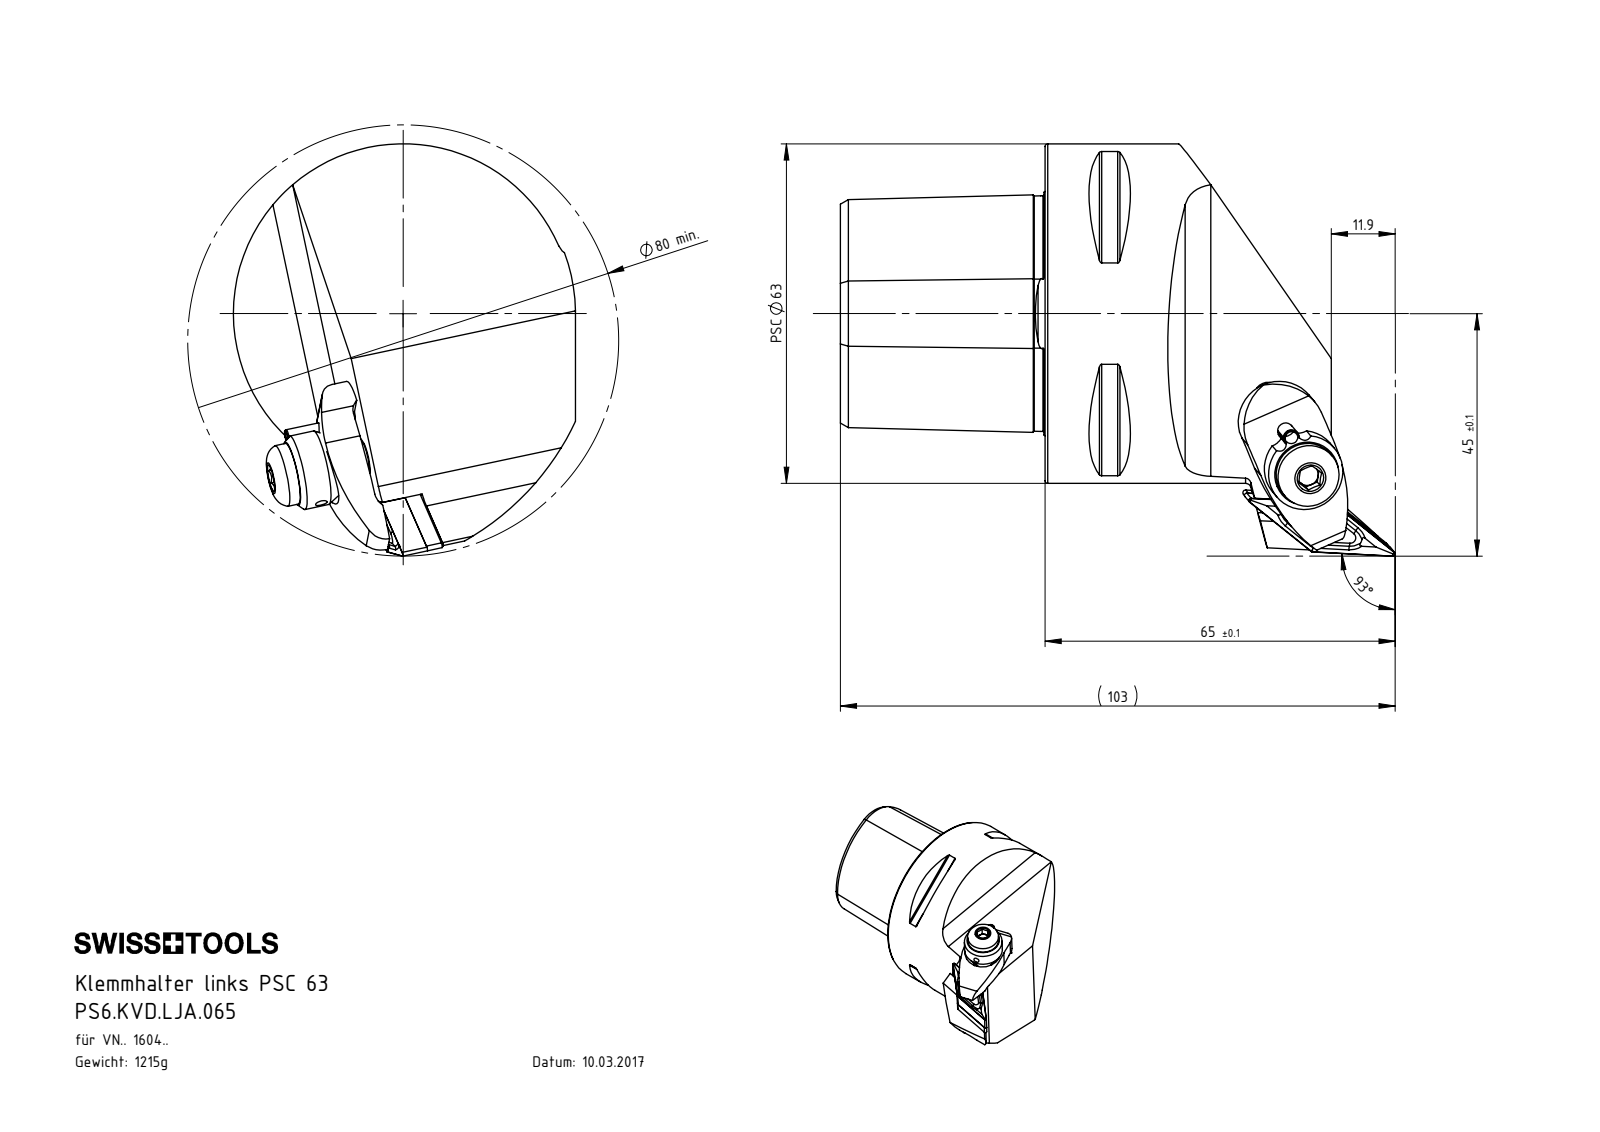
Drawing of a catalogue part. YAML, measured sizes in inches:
part_name: "KVT_MB_600_060; PS6.KVD.LJA.065; PS6-KVD.LJA.065_A; WCC-ER3.102.024_C (+7 more)"
step_written_by: "SolidWorks 2017 (AUTOMOTIVE_DESIGN)"
units: inches
bodies: {solids: 13, faces: 319, planar: 106, cylindrical: 89, other: 124}
overall_size: [4.055, 3.012, 2.5]
volume: 9.409
surface_area: 49.88
round_holes:
  - {diameter: 0.079, count: 3}
  - {diameter: 0.197, count: 3}
  - {diameter: 0.276, count: 2}
  - {diameter: 0.094, count: 1}
  - {diameter: 0.118, count: 1}
  - {diameter: 0.13, count: 1}
  - {diameter: 0.15, count: 1}
  - {diameter: 0.157, count: 1}
  - {diameter: 0.195, count: 1}
  - {diameter: 0.236, count: 1}
  - {diameter: 0.244, count: 1}
  - {diameter: 0.272, count: 1}
round_bosses_or_shafts:
  - {diameter: 0.236, count: 2}
  - {diameter: 0.157, count: 2}
  - {diameter: 0.118, count: 2}
  - {diameter: 2.48, count: 1}
  - {diameter: 0.551, count: 1}
  - {diameter: 0.453, count: 1}
  - {diameter: 0.268, count: 1}
  - {diameter: 0.244, count: 1}
partial_cylinders:
  - {radius: 0.02, count: 10}
  - {radius: 0.013, count: 6}
  - {radius: 0.023, count: 6}
  - {radius: 0.016, count: 4}
  - {radius: 0.059, count: 3}
  - {radius: 0.236, count: 3}
  - {radius: 0.079, count: 2}
  - {radius: 0.098, count: 2}
face_to_face_distances: [1.496, 0.98, 0.175, 0.125, 0.3, 1.063, 0.433, 0.363, 0.052, 0.352]
hole_center_spacings: [0.284, 0.563, 0.039, 0.039, 0.283, 0.284, 0.322, 0.323]
